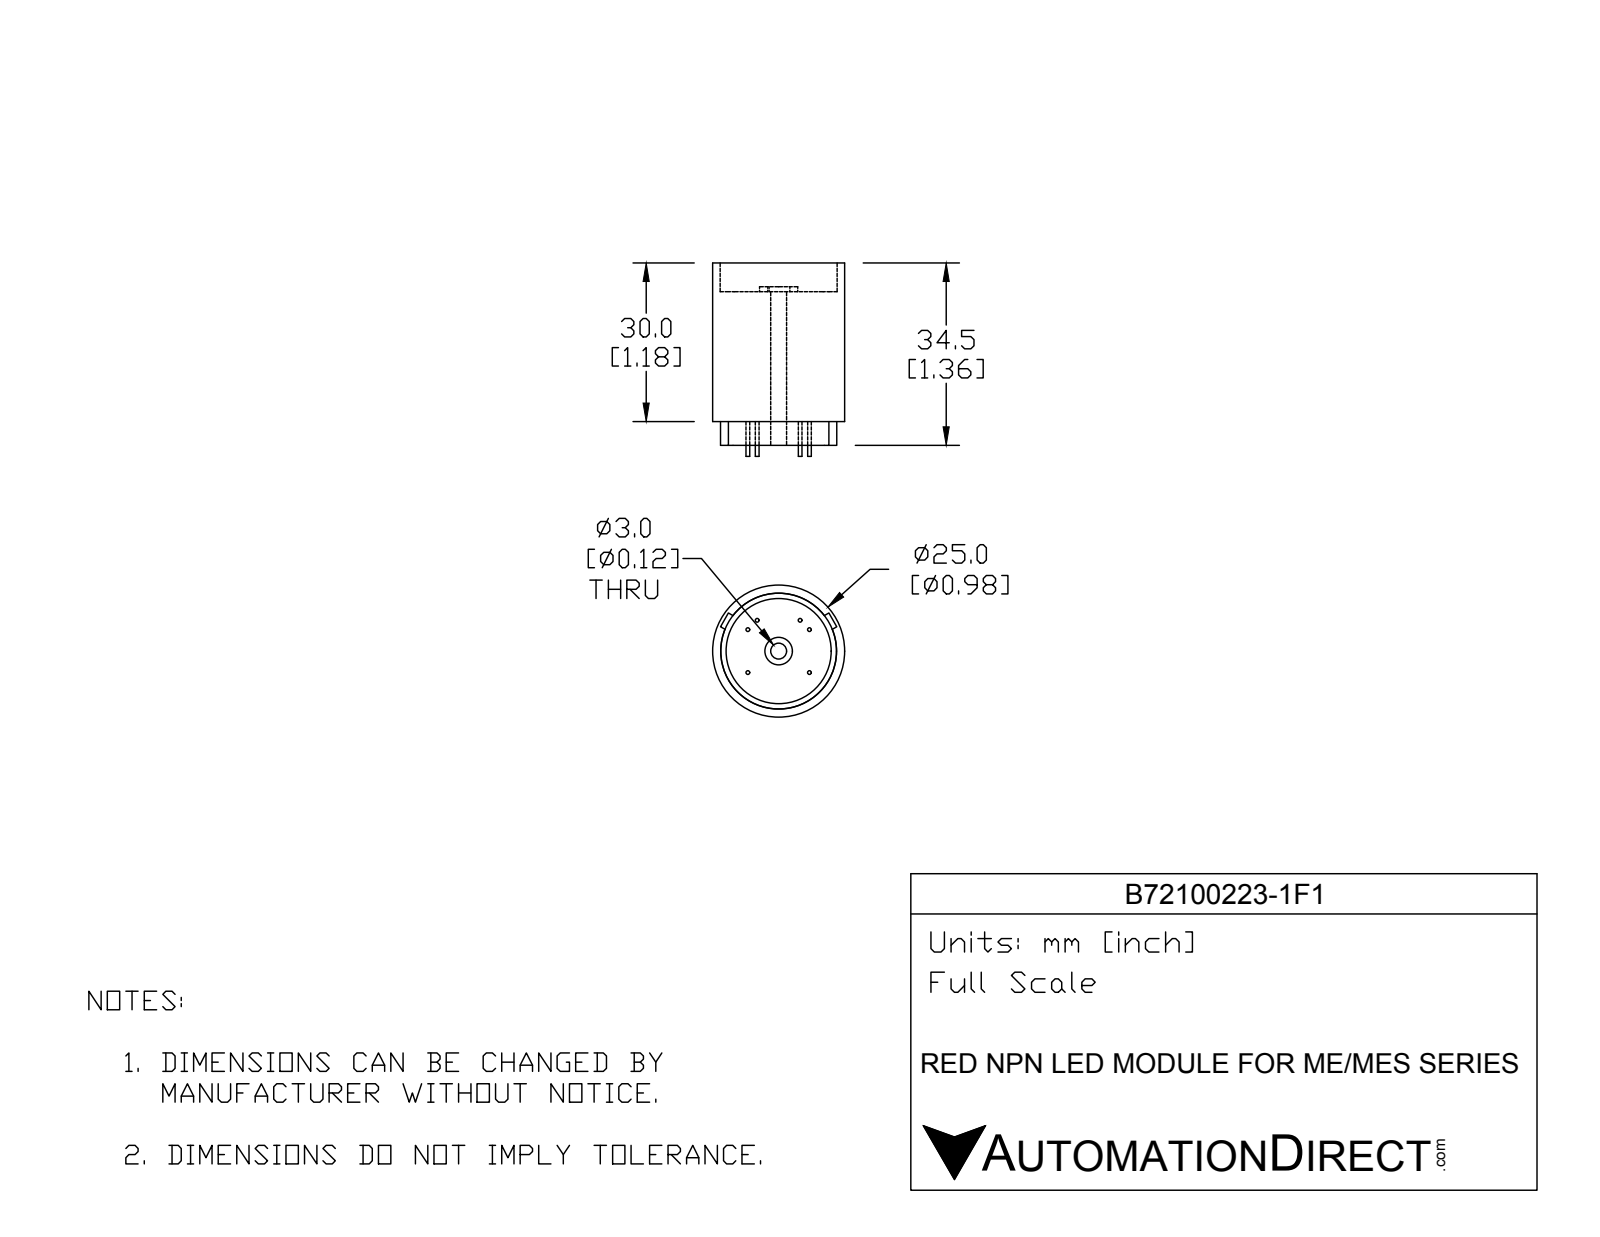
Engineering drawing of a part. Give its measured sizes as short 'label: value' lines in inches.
name: B72100223-1F1
written by: SolidWorks 2016 (AUTOMOTIVE_DESIGN)
unit: in
bodies: 9 solids, 69 faces (36 planar, 33 cylindrical, 0 other)
size: 1.441 × 0.984 × 0.984
volume: 0.791 in³; area: 7.57 in²
holes: 1× ⌀0.118, 1× ⌀0.166, 1× ⌀0.783, 1× ⌀0.846
bosses: 6× ⌀0.028, 1× ⌀0.984, 1× ⌀0.862, 1× ⌀0.284, 1× ⌀0.205
face distances: 0.967, 1.181, 0.214, 0.177, 1.144, 1.358, 1.004, 0.037, 0.12, 0.122
